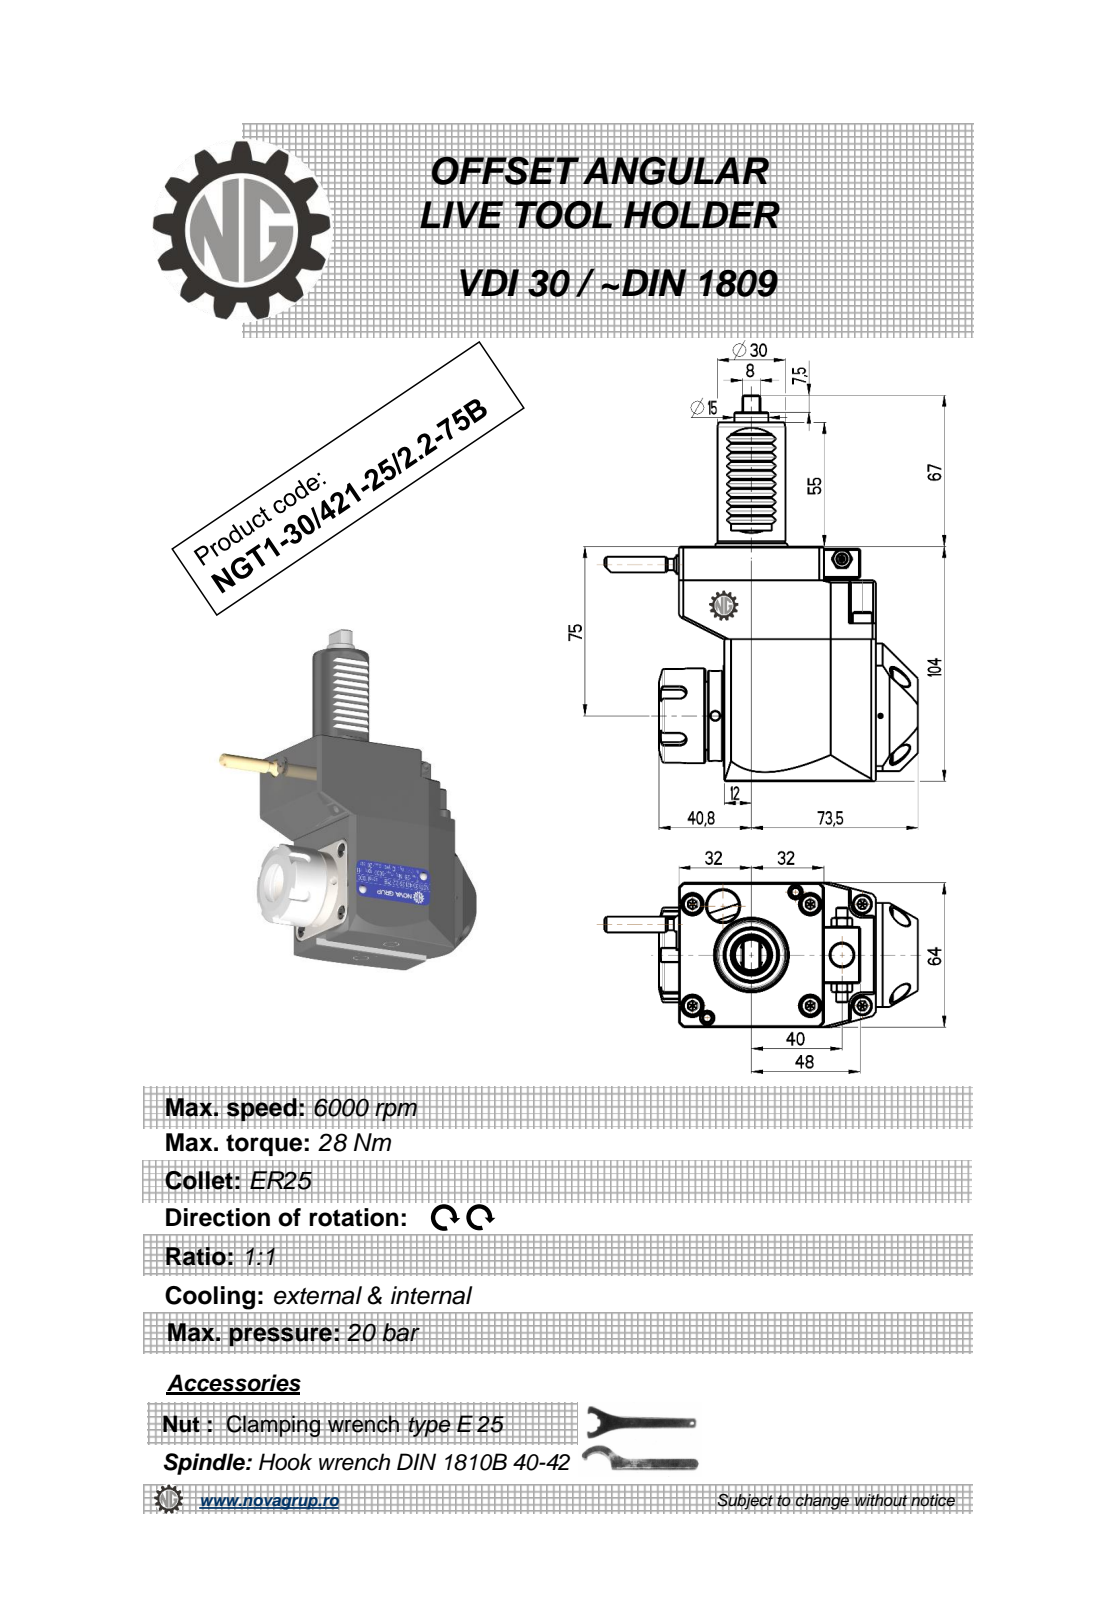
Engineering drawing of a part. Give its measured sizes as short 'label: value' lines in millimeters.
name: NGT1_30_421_25_2_2_75B
written by: PRO/ENGINEER BY PARAMETRIC TECHNOLOGY CORPORATION, 2010280 (CONFIG_CONTROL_DESIGN)
unit: mm
bodies: 1 solid, 450 faces (218 planar, 90 cylindrical, 142 other)
size: 171 × 138.38 × 65.4
volume: 567 644 mm³; area: 54 341 mm²
holes: 2× ⌀4, 1× ⌀2.5, 1× ⌀3, 1× ⌀4.2, 1× ⌀9.5, 1× ⌀10, 1× ⌀20.3
bosses: 2× ⌀8.96, 2× ⌀5, 1× ⌀42, 1× ⌀40, 1× ⌀33, 1× ⌀30, 1× ⌀15, 1× ⌀7
rounds: 12× R0.26, 10× R0.3, 5× R3, 2× R0.8, 2× R4, 1× R7.2, 1× R32
face distances: 64, 104, 87, 67.2, 19.8, 20, 15, 89, 67, 85.5
hole spacings: 13.54, 55.95, 68, 68.35, 89.22
